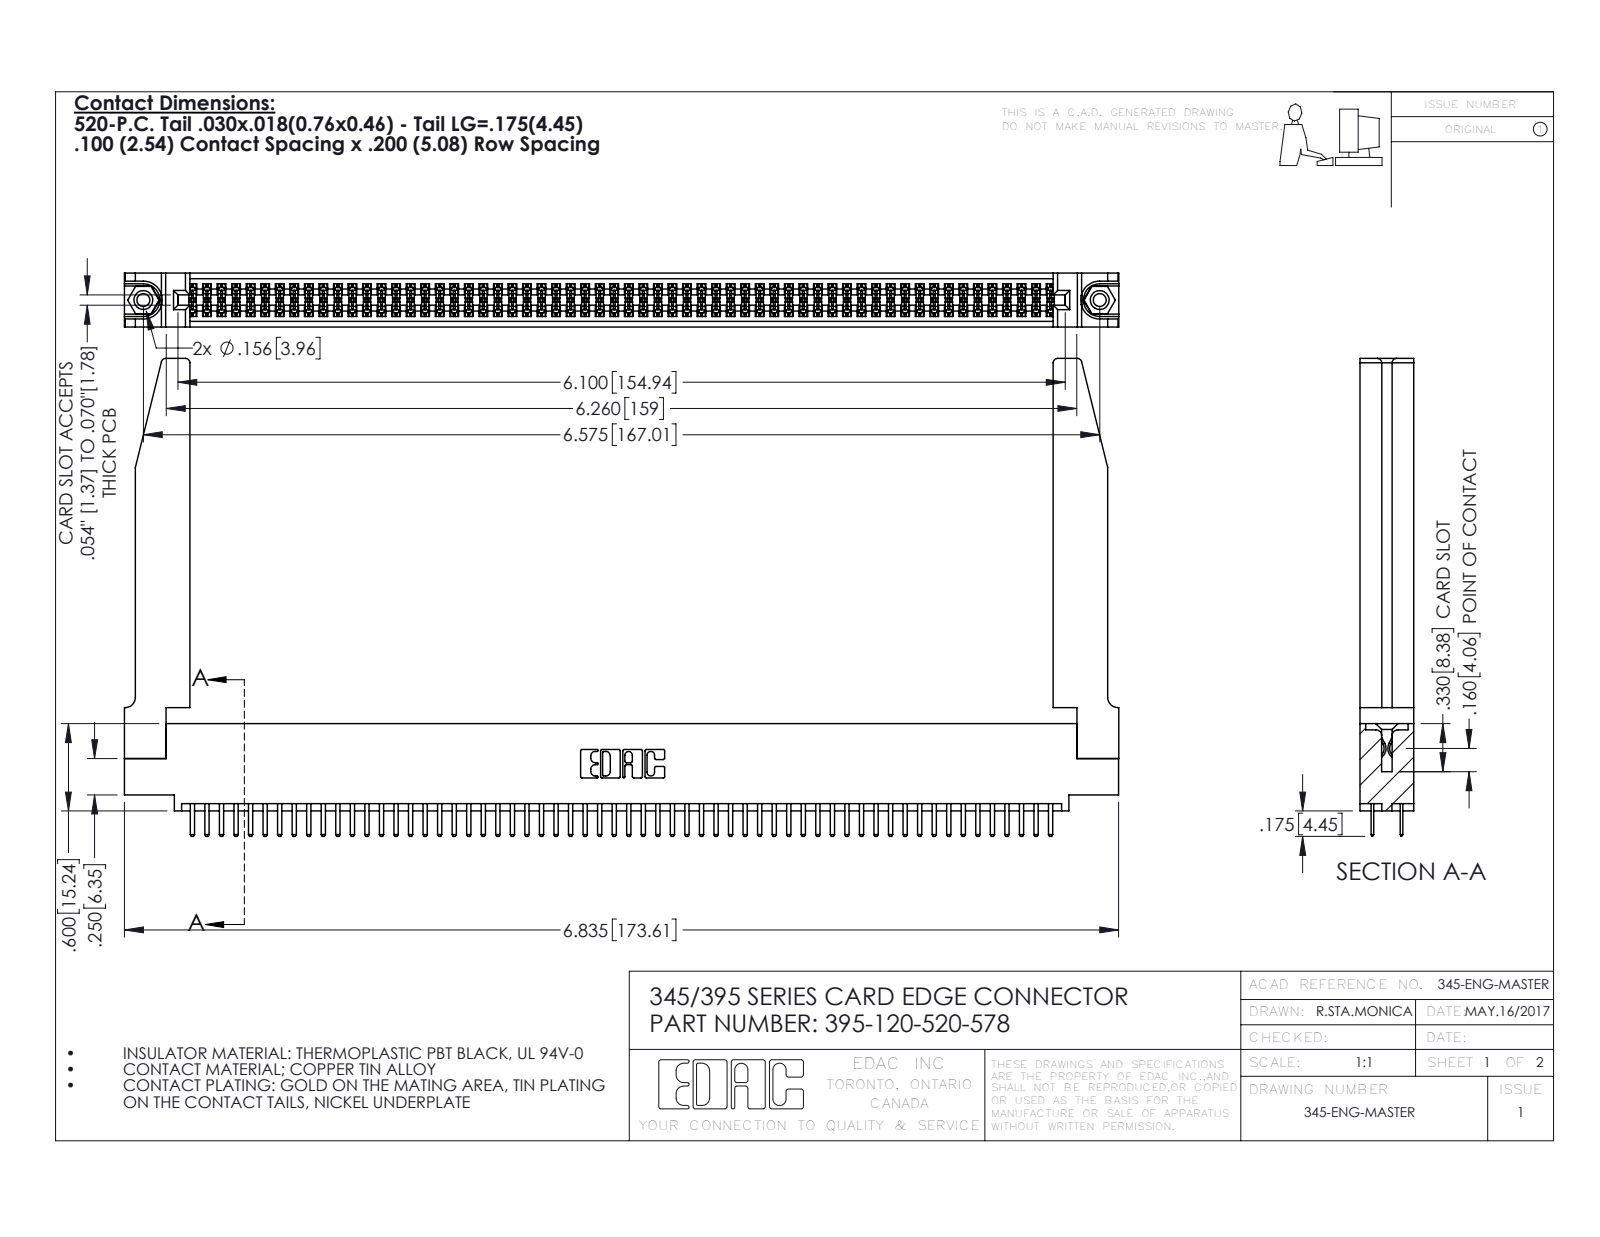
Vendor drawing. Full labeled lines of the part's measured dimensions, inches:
Part name (STEP PRODUCT): 345 Part_0.110 Offset - 0.156 Dia-TH; 345-220-078_345-220-078; 395-120-520-578; 345-250-001_345-250-001-102 (+1 more)
STEP written by: SolidWorks 2016 (CONFIG_CONTROL_DESIGN)
Units: inches
Bodies: 125 solids, 6844 faces (4426 planar, 2366 cylindrical, 52 other)
Overall size (bounding box): 6.836 × 3.285 × 0.37
Volume: 1.506 in³ · Surface area: 49.85 in²
Round holes (diameter × count): ⌀0.089 ×2, ⌀0.125 ×2, ⌀0.156 ×2, ⌀0.064 ×1
Round bosses / shafts (diameter × count): ⌀0.155 ×2
Partial cylindrical surfaces — rounded edges, fillets, slot ends (radius × count): R0.006 ×180, R0.01 ×124, R0.01 ×22, R0.03 ×8, R0.007 ×6, R0.031 ×6, R0.026 ×3, R0.014 ×2
Main face-to-face distances: 0.072, 0.37, 0.298, 0.2, 0.098, 0.272, 0.025, 0.225, 0.022, 0.072
Hole centre spacings: 0.27, 6.339, 6.575
